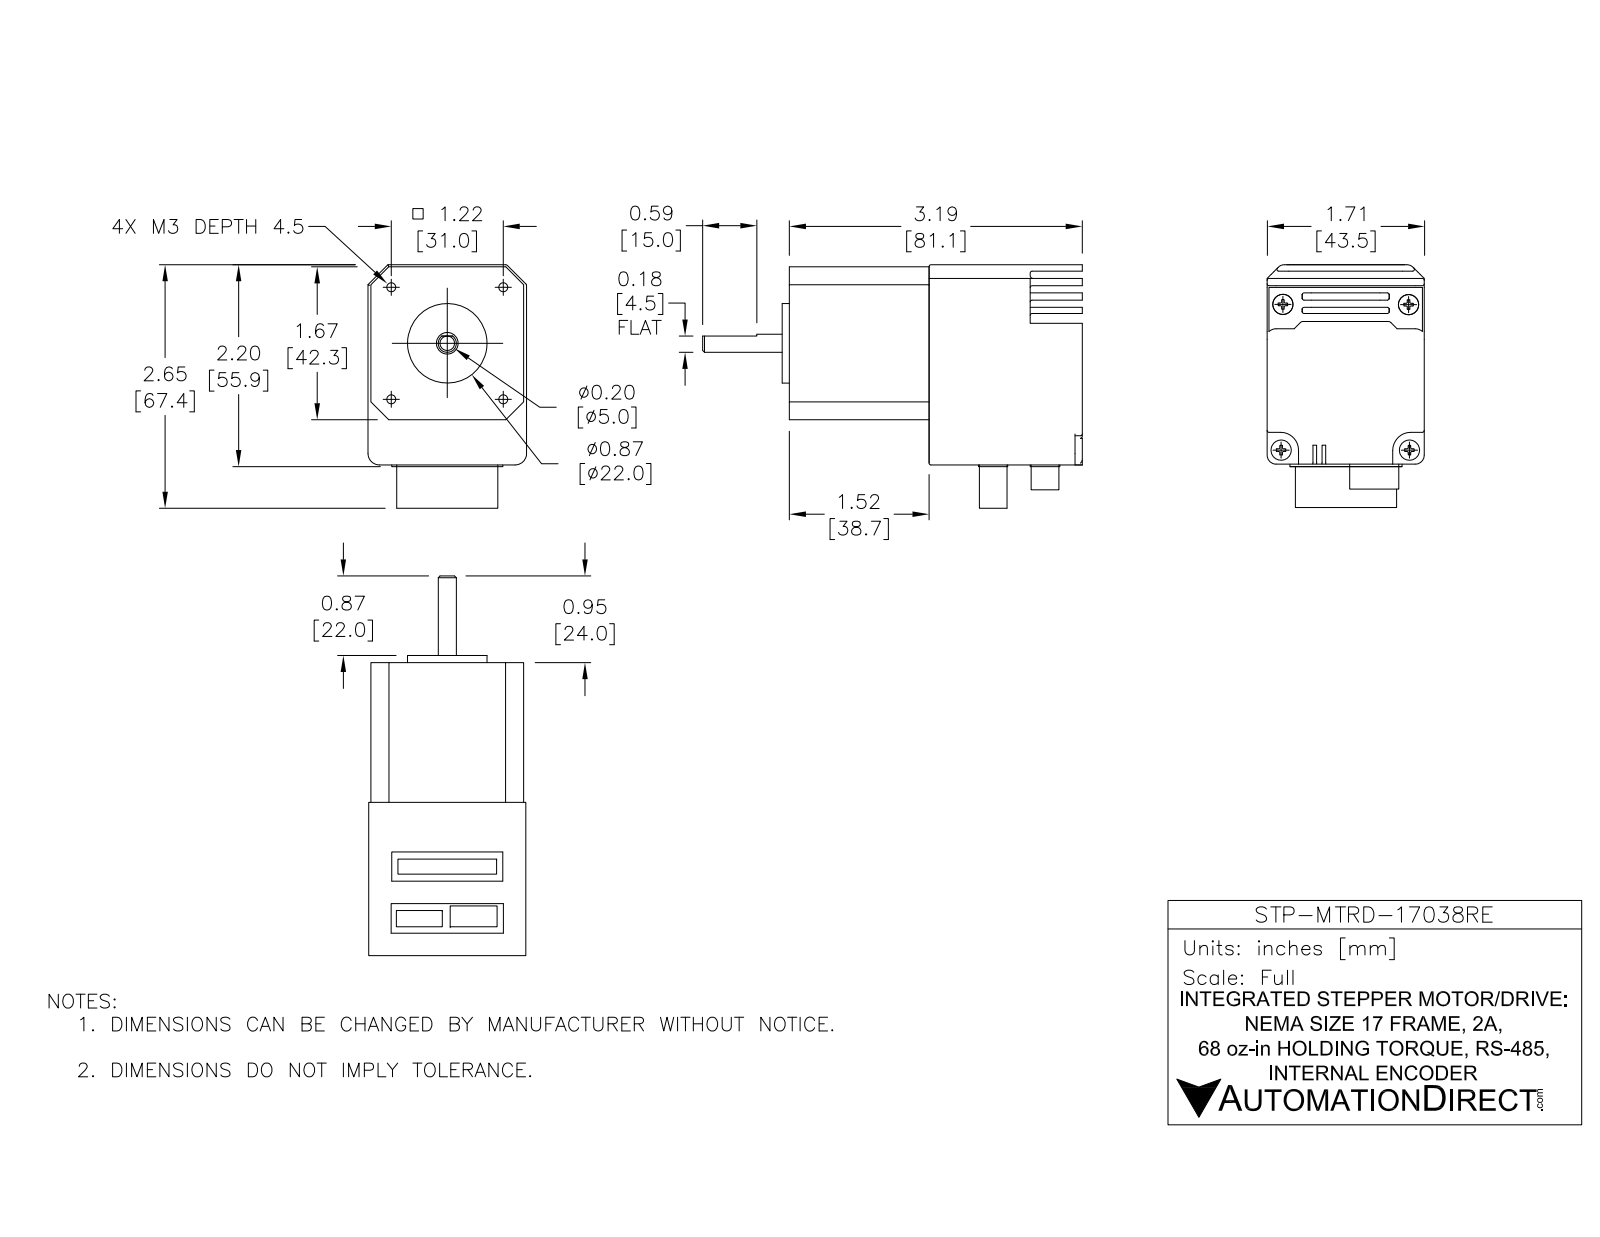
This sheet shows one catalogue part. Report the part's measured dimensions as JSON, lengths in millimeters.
{"part_name": "STP-MTRD-17038RE", "step_written_by": "SolidWorks 2017 (AUTOMOTIVE_DESIGN)", "units": "millimeters", "bodies": {"solids": 2, "faces": 396, "planar": 149, "cylindrical": 156, "other": 91}, "overall_size": [105.1, 55.85, 43.5], "volume_mm3": 155798, "surface_area_mm2": 24380, "round_holes": [[3, 4], [7.5, 1], [15, 1]], "round_bosses_or_shafts": [[5.6, 4], [22, 1], [5, 1]], "partial_cylinders_radius": [[0.5, 75], [2.5, 12], [0.68, 4], [10.96, 4], [25.37, 4], [5, 2], [0.75, 1]], "face_to_face_distances": [1.8, 2, 41.7, 39.9, 43.5, 81.1, 4, 41.1, 1.2, 55.2], "hole_center_spacings": [21.92, 31, 43.84]}
